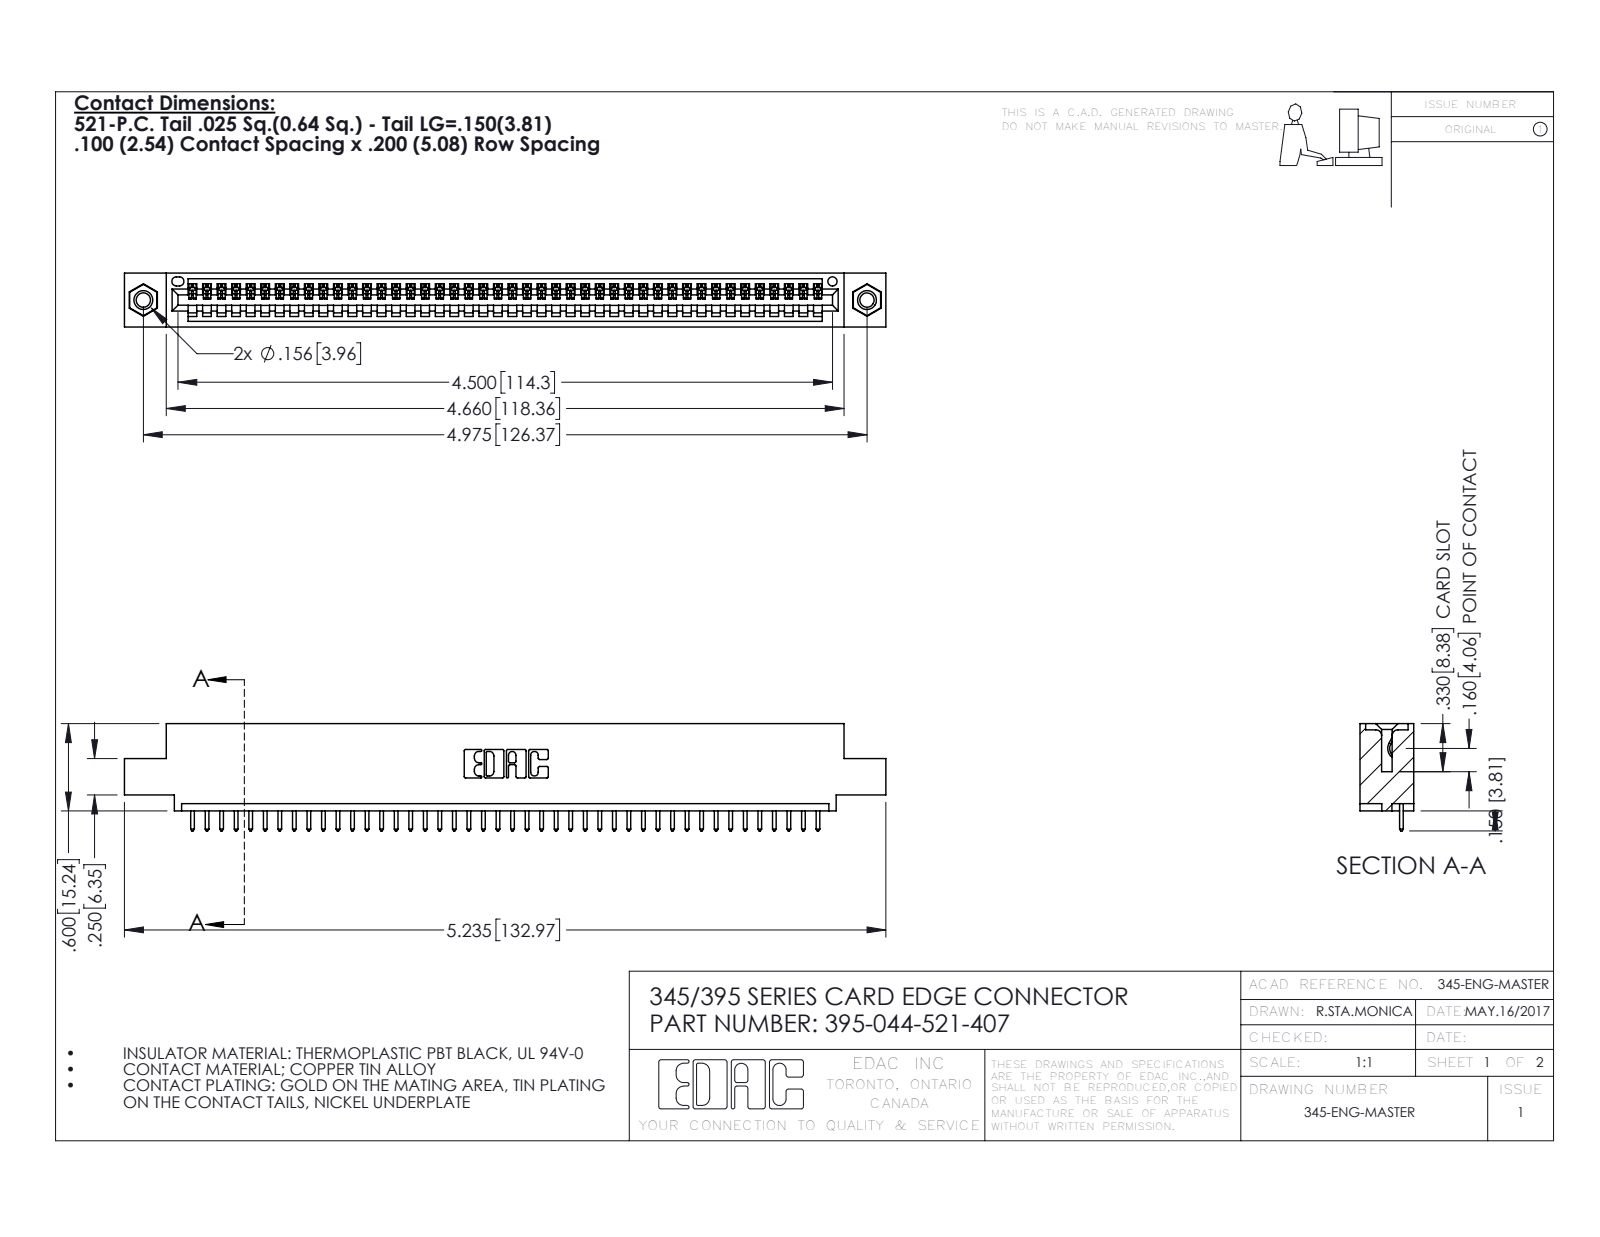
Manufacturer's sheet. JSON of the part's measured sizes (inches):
{"part_name": "345-292-001_345-293-121; 345 Part_0.110 Offset - 0.156 Dia-TI; 395-044-521-407; 345-250-001_345-250-005-103", "step_written_by": "SolidWorks 2016 (CONFIG_CONTROL_DESIGN)", "units": "inches", "bodies": {"solids": 47, "faces": 2742, "planar": 1876, "cylindrical": 850, "other": 16}, "overall_size": [5.235, 0.737, 0.37], "volume_in3": 0.759, "surface_area_in2": 25.07, "round_holes": [[0.098, 2], [0.125, 2], [0.156, 2], [0.064, 1]], "round_bosses_or_shafts": [[0.155, 2]], "partial_cylinders_radius": [[0.006, 88], [0.01, 88], [0.01, 22], [0.007, 6], [0.031, 6], [0.026, 3], [0.031, 2], [0.04, 2]], "face_to_face_distances": [0.072, 0.298, 0.37, 0.2, 0.098, 0.272, 0.025, 0.225, 0.149, 0.072], "hole_center_spacings": [0.27, 4.739, 4.975]}
